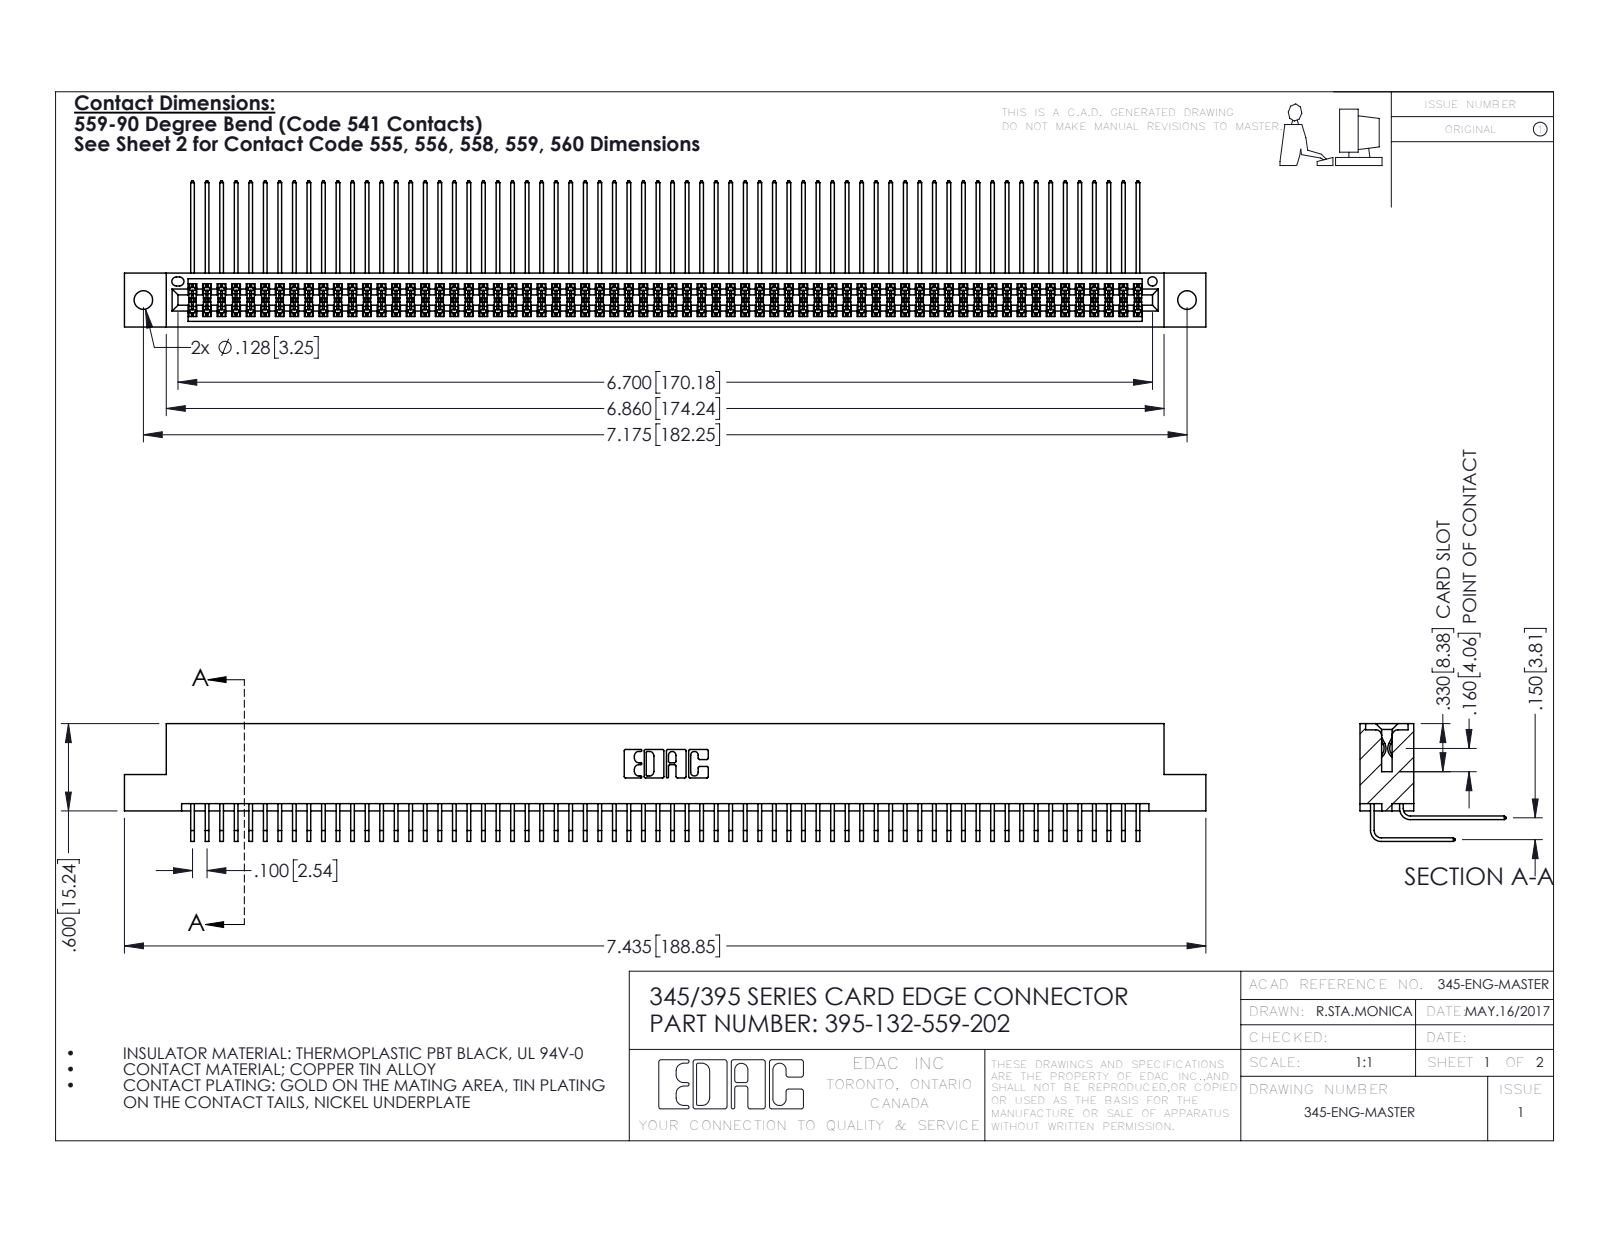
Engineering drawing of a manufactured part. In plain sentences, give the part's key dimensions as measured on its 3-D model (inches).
The part is named "345-292-001_558 559 Tail - 1; 345-292-001_559 Tail - 2; 395-132-559-202; 345 Part_Flush Mounting Lugs - 0.128 Dia". Its 3-D file was written by "SolidWorks 2016 (CONFIG_CONTROL_DESIGN)". It is 133 solids with 6990 faces: 4700 planar, 2290 cylindrical and 0 other. Overall it measures 7.435 by 1.005 by 0.809 inches. Its volume is 1.177 cubic inches and its surface area 50.05 square inches. Round holes: 2 of diameter 0.128, 1 of diameter 0.064. Partial cylindrical surfaces (rounded edges, fillets, slot ends): 199 of radius 0.006, 22 of radius 0.01, 6 of radius 0.007, 6 of radius 0.031, 3 of radius 0.026, 2 of radius 0.014, 2 of radius 0.019, 2 of radius 0.022. The main face-to-face distances are 0.072, 0.298, 0.2, 0.37, 0.098, 0.272, 0.025, 0.225, 0.175, 0.15. The hole center spacings are 0.27, 6.939, 7.175.
